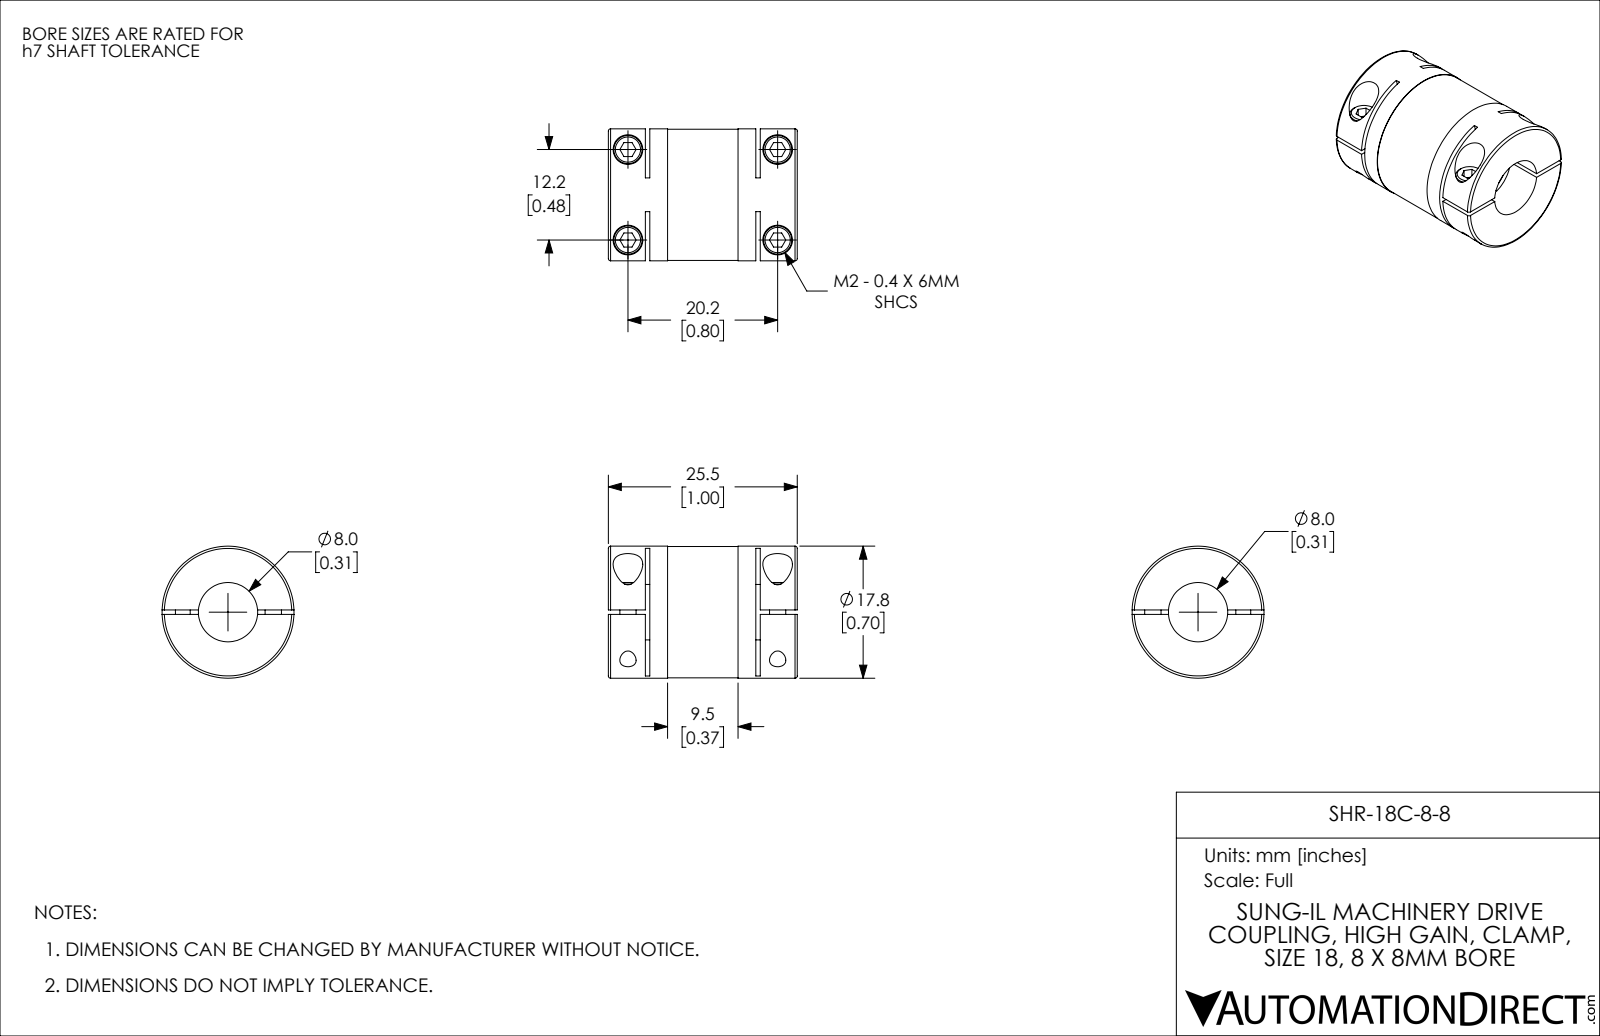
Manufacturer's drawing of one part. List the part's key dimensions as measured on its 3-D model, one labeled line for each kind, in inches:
Part name (STEP PRODUCT): SHR-18C-8-8
STEP written by: SolidWorks 2021 (CONFIG_CONTROL_DESIGN)
Units: inches
Bodies: 1 solid, 146 faces (70 planar, 56 cylindrical, 20 other)
Overall size (bounding box): 1.004 × 0.701 × 0.701
Volume: 0.265 in³ · Surface area: 5.913 in²
Round holes (diameter × count): ⌀0.087 ×4, ⌀0.157 ×4, ⌀0.315 ×1, ⌀0.394 ×1
Round bosses / shafts (diameter × count): ⌀0.15 ×4, ⌀0.079 ×2, ⌀0.701 ×1, ⌀0.697 ×1
Partial cylindrical surfaces — rounded edges, fillets, slot ends (radius × count): R1.378 ×2
Main face-to-face distances: 0.024, 0.22, 0.783, 0.197, 0.807, 0.587, 1.004, 0.563, 0.61, 0.689
Hole centre spacings: 0.48, 0.795, 0.929
